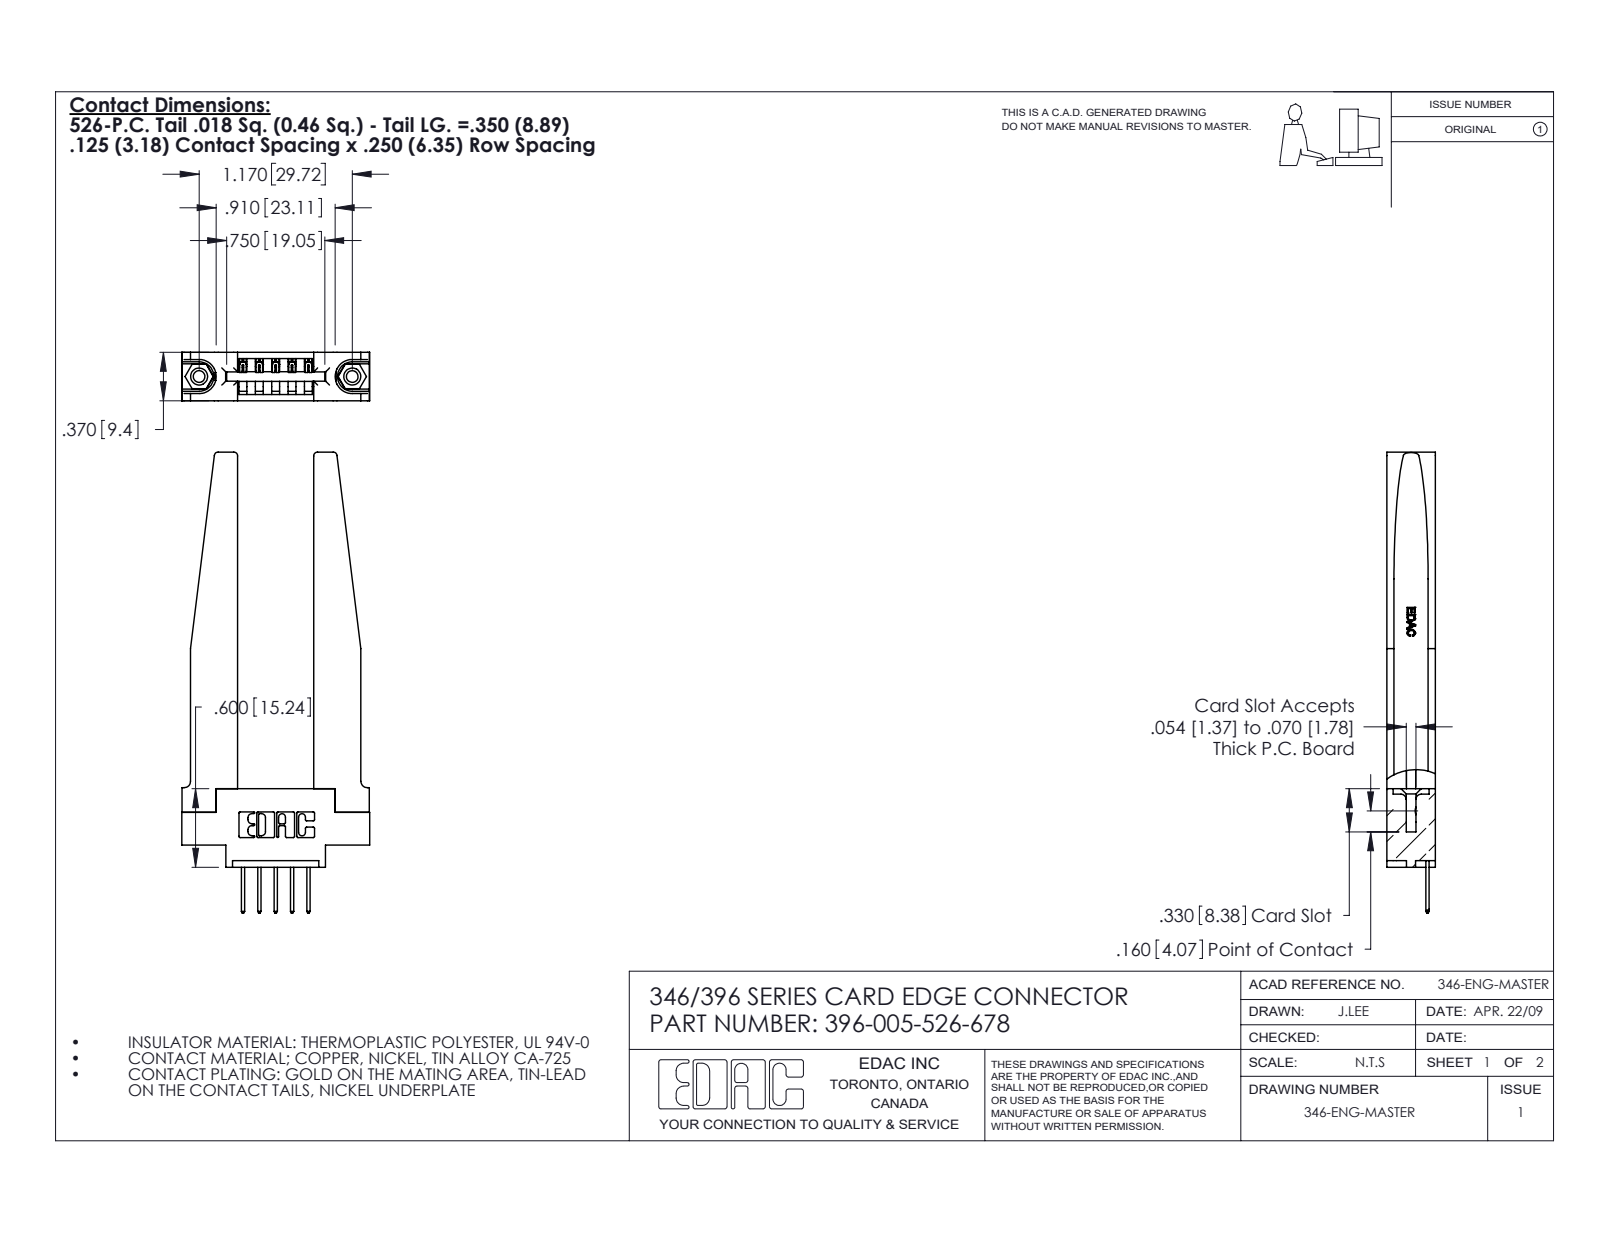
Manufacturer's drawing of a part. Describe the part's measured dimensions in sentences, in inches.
The part is named "346 Part_0.170 Offset - 0.156 Dia-TH; 396-005-526-678; 345-292-001_345-293-126; 345-250-001_345-250-001-102 (+1 more)". Its 3-D file was written by "SolidWorks 2020 (CONFIG_CONTROL_DESIGN)". It is 10 solids with 664 faces: 436 planar, 176 cylindrical and 52 other. Overall it measures 3.52 by 1.435 by 0.37 inches. Its volume is 0.608 cubic inches and its surface area 15.73 square inches. Round holes: 2 of diameter 0.089, 2 of diameter 0.125, 2 of diameter 0.156, 1 of diameter 0.064. Round bosses or shafts: 2 of diameter 0.155. Partial cylindrical surfaces (rounded edges, fillets, slot ends): 22 of radius 0.01, 10 of radius 0.006, 10 of radius 0.01, 8 of radius 0.03, 6 of radius 0.007, 6 of radius 0.031, 3 of radius 0.026, 2 of radius 0.031. The main face-to-face distances are 0.37, 0.15, 0.22, 0.581, 0.25, 0.072, 0.148, 0.102, 0.048, 0.322. The hole center spacings are 0.246, 0.969, 1.17.
